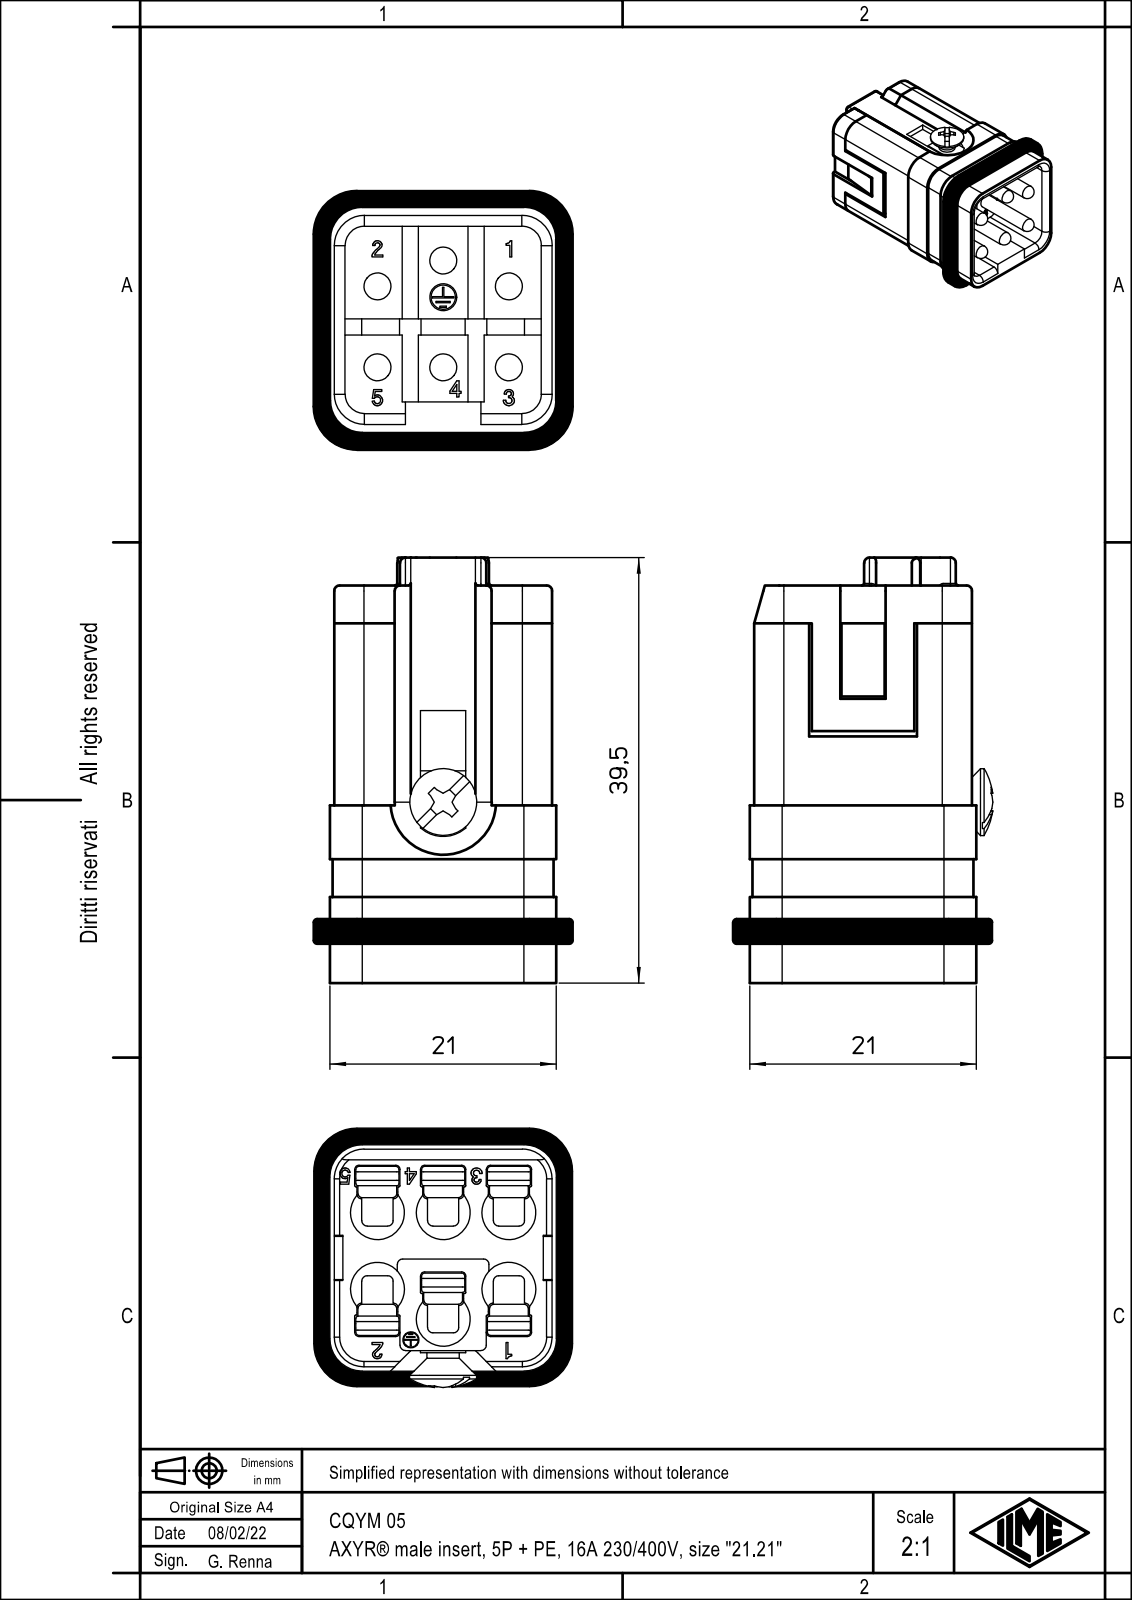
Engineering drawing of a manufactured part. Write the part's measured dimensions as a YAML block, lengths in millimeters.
part_name: "CQYM_05"
step_written_by: "Creo Elements/Direct Modeling 20.1B 02-Apr-2019 (C) Parametric Technology GmbH (AUTOMOTIVE_DESIGN)"
units: millimeters
bodies: {solids: 1, faces: 933, planar: 562, cylindrical: 262, other: 109}
overall_size: [39.6, 24.07, 24]
volume: 10619
surface_area: 7713
round_holes:
  - {diameter: 2.5, count: 1}
round_bosses_or_shafts:
  - {diameter: 2.5, count: 6}
  - {diameter: 6.2, count: 1}
  - {diameter: 3, count: 1}
  - {diameter: 2.26, count: 1}
partial_cylinders:
  - {radius: 0.2, count: 52}
  - {radius: 0.4, count: 36}
  - {radius: 0.5, count: 26}
  - {radius: 0.3, count: 20}
  - {radius: 0.1, count: 12}
  - {radius: 2.75, count: 8}
  - {radius: 2.5, count: 6}
  - {radius: 1, count: 4}
face_to_face_distances: [1.4, 0.4, 19.2, 20.6, 1.5, 1, 20.2, 8.7, 1.9, 8.6]
